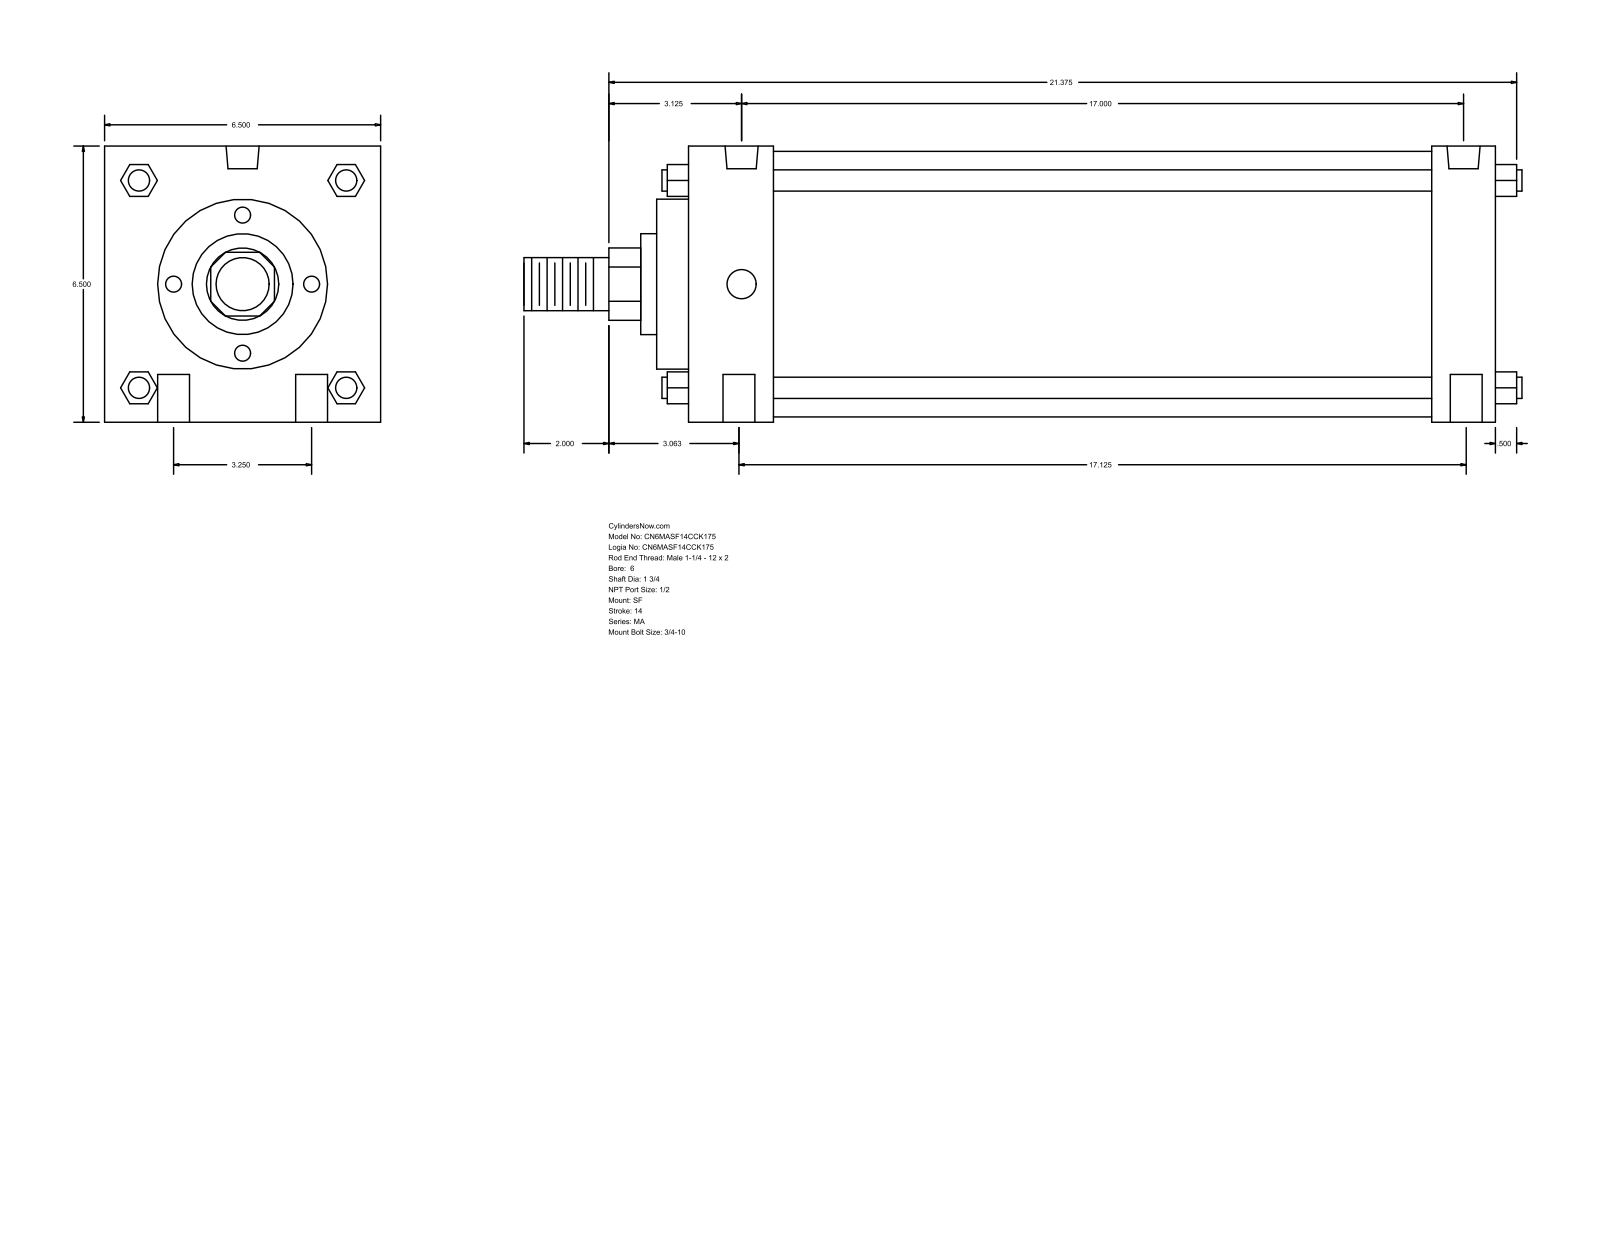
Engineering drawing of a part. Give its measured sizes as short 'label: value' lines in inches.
name: MA_SF__0600_1.75
written by: GSSL Pune (CONFIG_CONTROL_DESIGN)
unit: in
bodies: 0 solids, 126 faces (95 planar, 31 cylindrical, 0 other)
size: 23.5 × 6.5 × 6.5
holes: 4× ⌀0.75, 2× ⌀0.687, 2× ⌀0.778
bosses: 4× ⌀0.5, 1× ⌀6.25, 1× ⌀4, 1× ⌀2.375, 1× ⌀1.75, 1× ⌀1.25
rounds: 1× R0.852
face distances: 6.5, 19, 0.75, 2, 17.5, 1.5, 15.5, 17, 2.75, 18.25
hole spacings: 1.626, 3.25, 17, 17.125, 17.139, 17.14, 17.43
